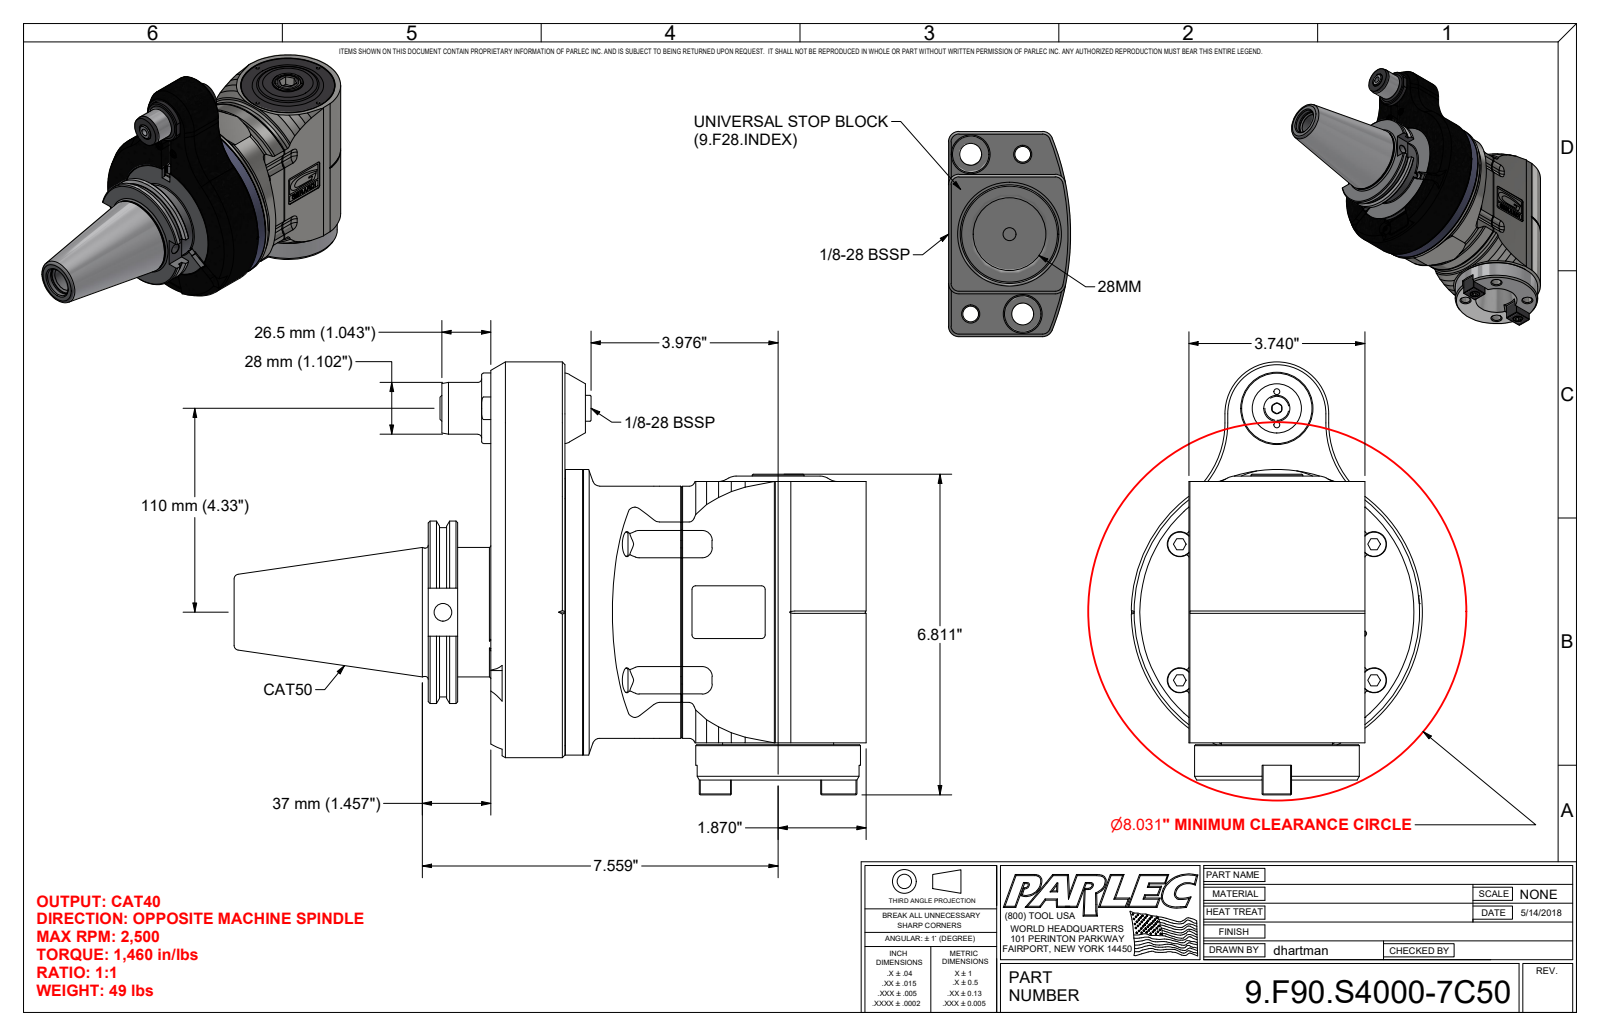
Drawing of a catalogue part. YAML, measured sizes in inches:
part_name: "9.F90.S4000-7C50; 9_GA3_451_2_7_C50; 9FL3ATC; 9CT503ATC (+2 more)"
step_written_by: "Autodesk Inventor 2022 (AUTOMOTIVE_DESIGN)"
units: inches
bodies: {solids: 5, faces: 866, planar: 378, cylindrical: 232, other: 256}
overall_size: [13.429, 9.193, 6.181]
volume: 28.79
surface_area: 542.3
round_holes:
  - {diameter: 0.413, count: 21}
  - {diameter: 0.126, count: 6}
  - {diameter: 0.266, count: 4}
  - {diameter: 0.335, count: 4}
  - {diameter: 0.404, count: 4}
  - {diameter: 0.531, count: 4}
  - {diameter: 0.165, count: 2}
  - {diameter: 0.209, count: 2}
  - {diameter: 0.236, count: 2}
  - {diameter: 0.315, count: 2}
  - {diameter: 0.098, count: 1}
  - {diameter: 0.197, count: 1}
round_bosses_or_shafts:
  - {diameter: 0.512, count: 4}
  - {diameter: 0.315, count: 4}
  - {diameter: 0.394, count: 3}
  - {diameter: 1.102, count: 2}
  - {diameter: 0.256, count: 2}
  - {diameter: 0.098, count: 2}
  - {diameter: 6.063, count: 1}
  - {diameter: 5.669, count: 1}
partial_cylinders:
  - {radius: 0.079, count: 12}
  - {radius: 0.276, count: 12}
  - {radius: 0.118, count: 6}
  - {radius: 0.039, count: 4}
  - {radius: 0.157, count: 4}
  - {radius: 0.197, count: 4}
  - {radius: 0.394, count: 4}
  - {radius: 0.098, count: 2}
face_to_face_distances: [0.197, 1.378, 1.181, 0.039, 0.236, 0.531, 0.61, 3.74, 0.768, 1.142]
hole_center_spacings: [2.52, 2.244, 1.098, 2.615, 0.464, 1.144, 5.039, 0.702]
